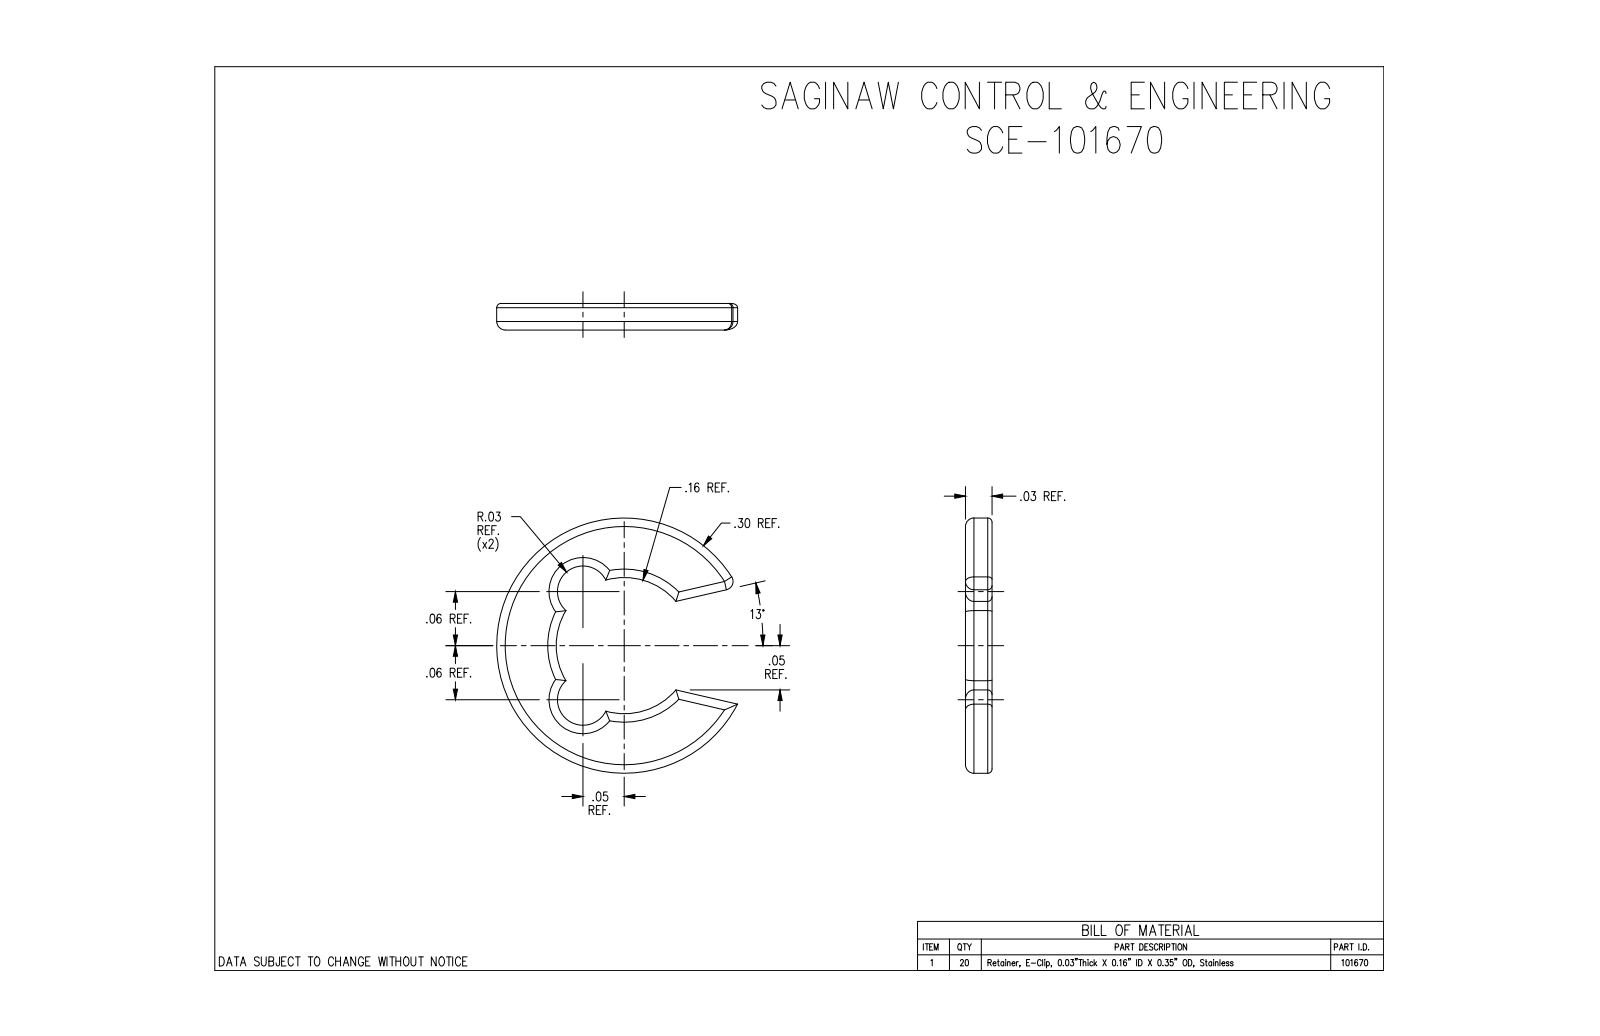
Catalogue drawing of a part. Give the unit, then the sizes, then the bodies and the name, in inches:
Units: inches
Overall size (bounding box): 0.3 × 0.283 × 0.031
Round bosses / shafts (diameter × count): ⌀0.3 ×1
Partial cylindrical surfaces — rounded edges, fillets, slot ends (radius × count): R0.01 ×3, R0.005 ×2, R0.03 ×2, R0.08 ×1
Main face-to-face distances: 0.031
Volume: 0.001 in³ · Surface area: 0.112 in²
Bodies: 1 solid, 29 faces (4 planar, 11 cylindrical, 14 other)
Part name (STEP PRODUCT): SCE-101670
STEP written by: SolidWorks 2019 (AUTOMOTIVE_DESIGN)
